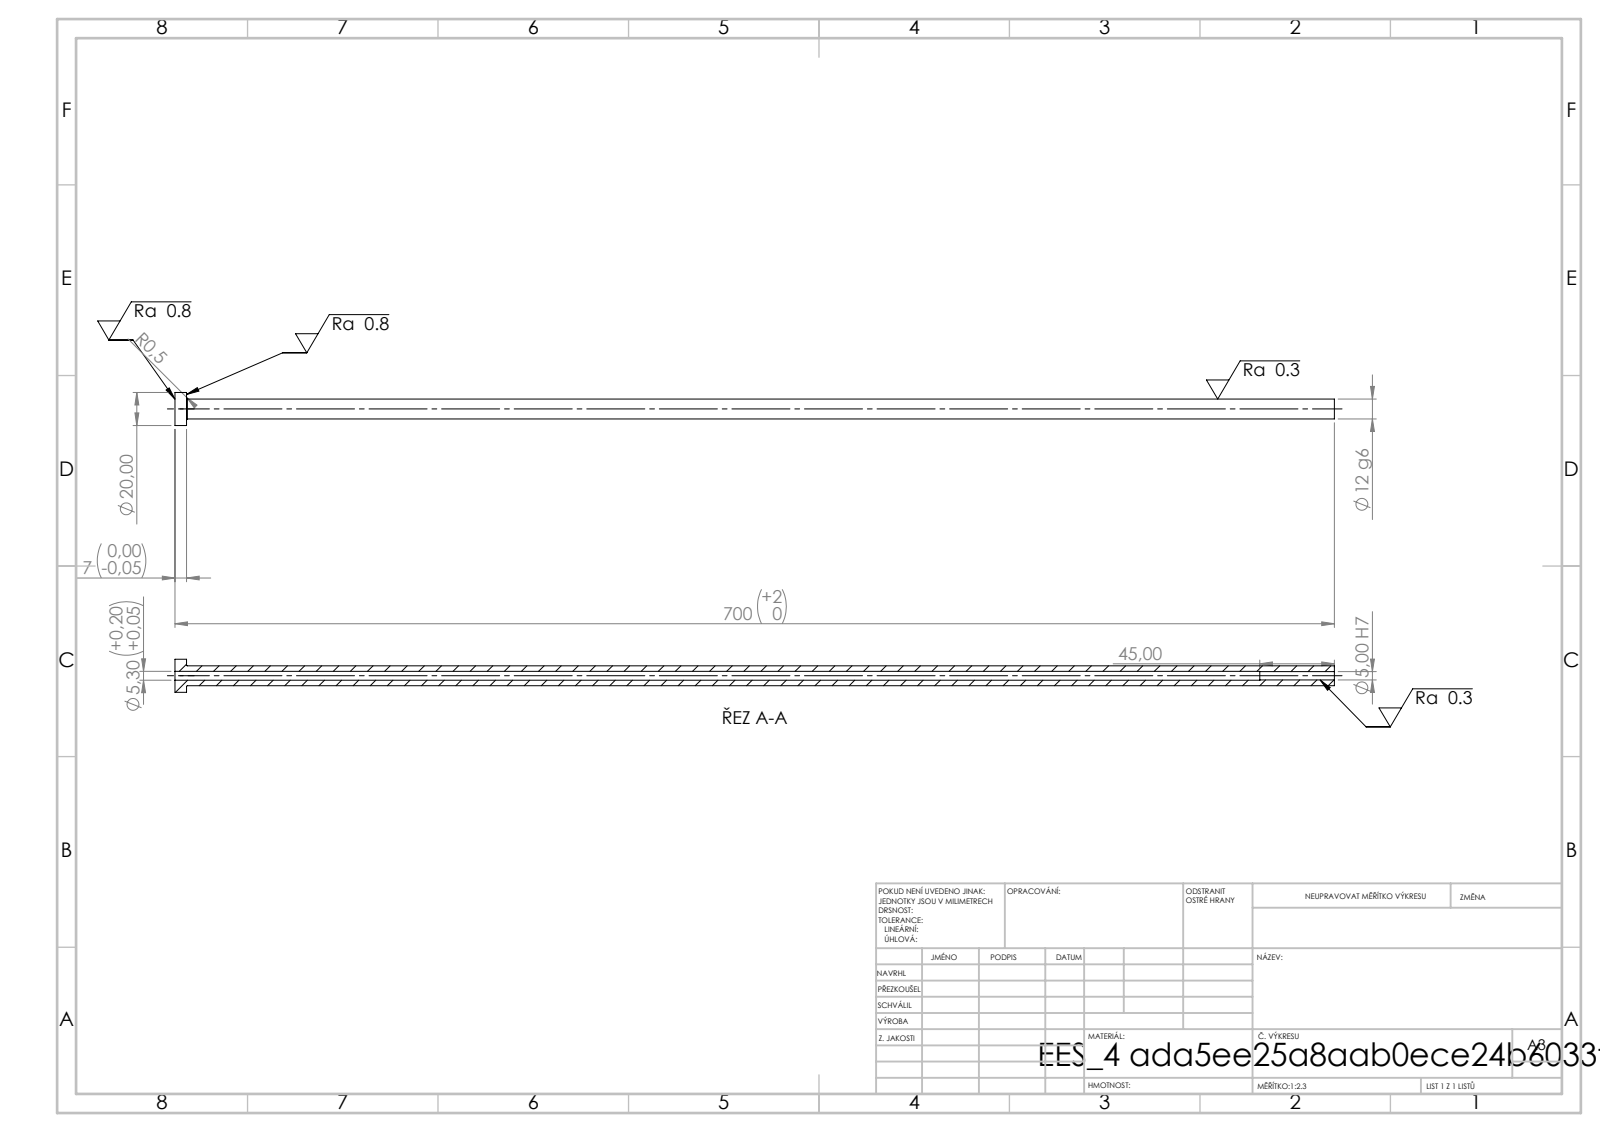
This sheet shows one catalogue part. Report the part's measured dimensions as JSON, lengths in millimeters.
{"step_written_by": "SolidWorks 2019 (CONFIG_CONTROL_DESIGN)", "units": "millimeters", "bodies": {"solids": 1, "faces": 14, "planar": 4, "cylindrical": 8, "other": 2}, "overall_size": [700, 20, 20], "volume_mm3": 65244, "surface_area_mm2": 38759, "round_holes": [[5, 1], [5.3, 1]], "round_bosses_or_shafts": [[20, 1], [12, 1]], "face_to_face_distances": [7, 700, 693, 655, 648, 45]}
